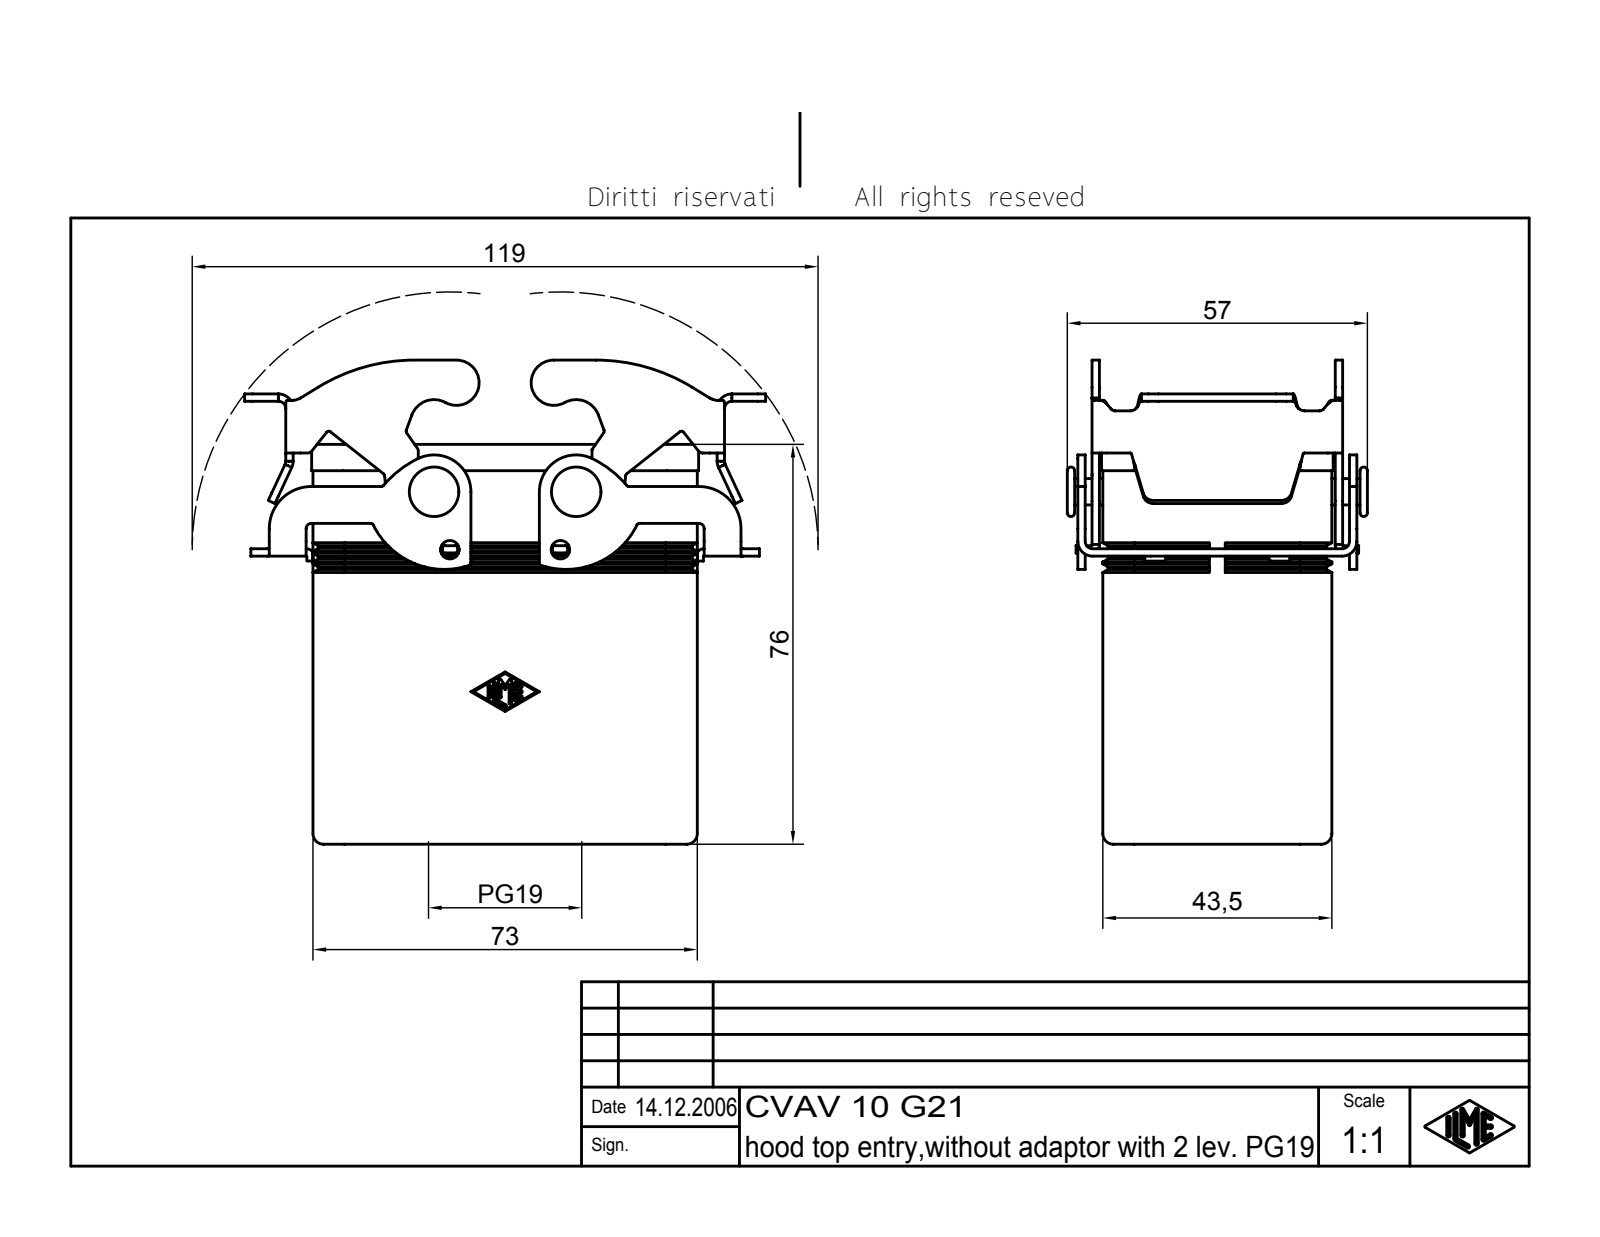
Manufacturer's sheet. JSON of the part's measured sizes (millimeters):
{"part_name": "CVAV 10 G21", "step_written_by": "Autodesk Inventor 7 (AUTOMOTIVE_DESIGN)", "units": "millimeters", "bodies": {"solids": 3, "faces": 706, "planar": 205, "cylindrical": 182, "other": 319}, "overall_size": [98.97, 91.91, 57], "volume_mm3": 82246, "surface_area_mm2": 55473, "round_holes": [[3.5, 2], [26.78, 1]], "round_bosses_or_shafts": [[5, 2], [3.2, 2]], "partial_cylinders_radius": [[0.5, 18], [0.25, 16], [1, 14], [1.5, 12], [2, 12], [1.4, 10], [2.8, 10], [6, 8]], "face_to_face_distances": [3, 40.5, 43.5, 37.5, 1.4, 70, 8.5, 73, 11.75, 2.7], "hole_center_spacings": [21]}
